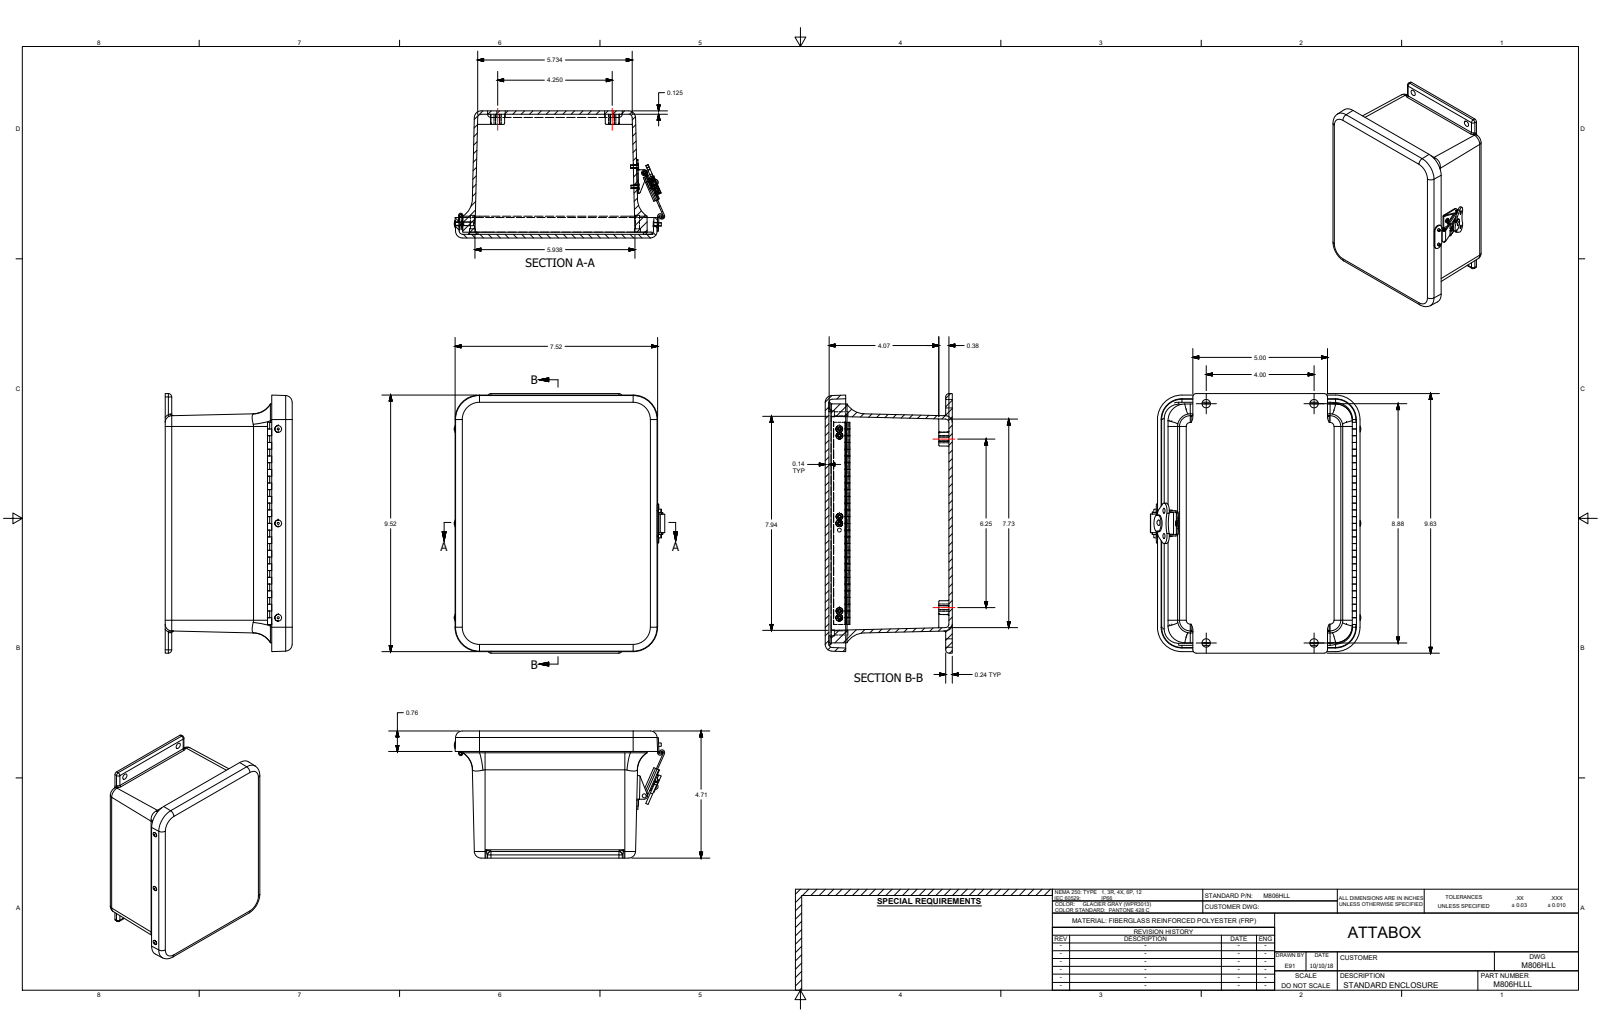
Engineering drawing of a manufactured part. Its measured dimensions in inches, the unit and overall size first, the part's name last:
Units: inches
Overall size (bounding box): 9.63 × 7.814 × 4.715
Round holes (diameter × count): ⌀0.14 ×11, ⌀0.104 ×10, ⌀0.152 ×8, ⌀0.131 ×6, ⌀0.159 ×4, ⌀0.218 ×4, ⌀0.312 ×4, ⌀0.13 ×2, ⌀0.133 ×2, ⌀0.187 ×2, ⌀0.191 ×2, ⌀0.067 ×1
Round bosses / shafts (diameter × count): ⌀0.125 ×6, ⌀0.125 ×5, ⌀0.27 ×4, ⌀0.66 ×1, ⌀0.582 ×1, ⌀0.525 ×1, ⌀0.286 ×1, ⌀0.213 ×1
Partial cylindrical surfaces — rounded edges, fillets, slot ends (radius × count): R0.031 ×36, R0.125 ×17, R0.25 ×9, R0.015 ×8, R0.074 ×8, R0.06 ×7, R0.011 ×4, R0.02 ×4
Main face-to-face distances: 0.125, 0.135, 4.58, 4.715, 0.125, 4.455, 4.589, 0.135, 4.5, 4.375
Hole centre spacings: 3.5, 7.558, 1.318, 7.249, 7.564, 8.614, 1.326, 3
Volume: 44.43 in³ · Surface area: 619.7 in²
Bodies: 30 solids, 817 faces (317 planar, 327 cylindrical, 173 other)
Part name (STEP PRODUCT): M806HLL
STEP written by: SolidWorks 2018 (AUTOMOTIVE_DESIGN)
